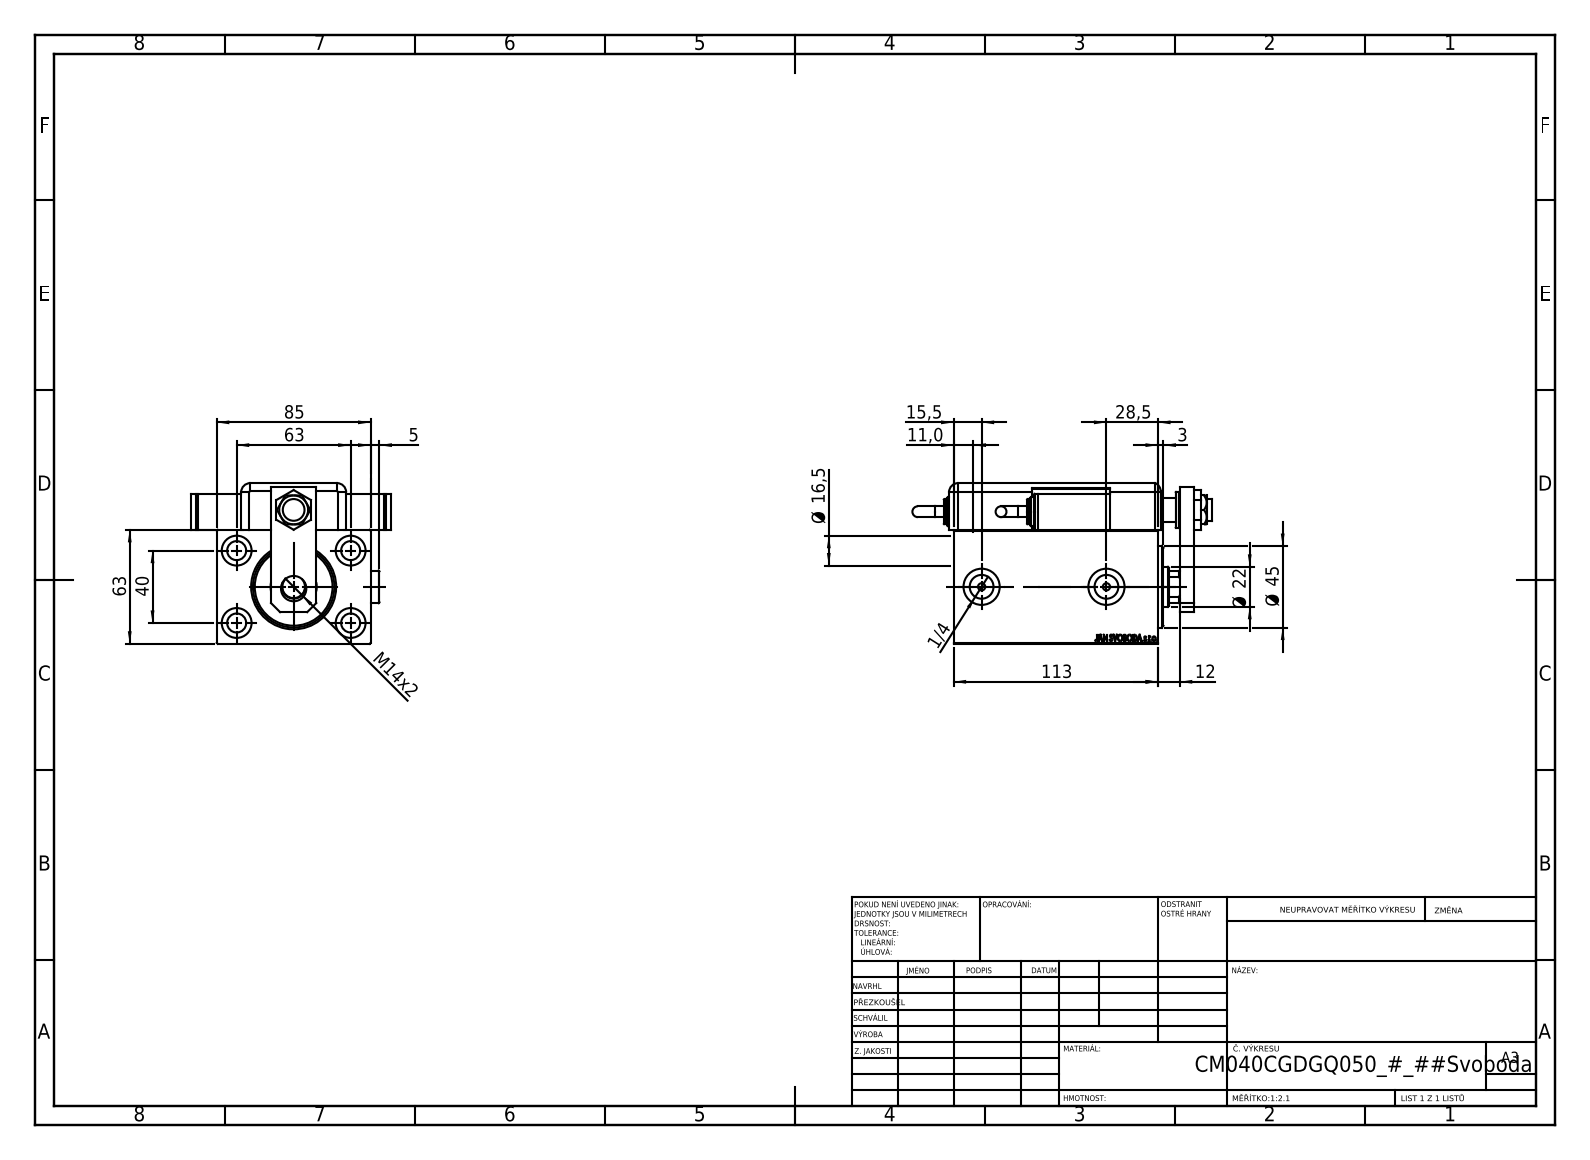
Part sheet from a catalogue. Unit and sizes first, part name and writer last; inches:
Units: inches
Overall size (bounding box): 6.514 × 4.37 × 3.496
Round holes (diameter × count): ⌀0.157 ×4, ⌀0.413 ×4, ⌀0.65 ×4, ⌀0.315 ×2, ⌀0.518 ×2, ⌀0.551 ×2, ⌀0.787 ×2, ⌀0.472 ×1, ⌀0.492 ×1, ⌀0.512 ×1, ⌀0.866 ×1, ⌀1.004 ×1
Round bosses / shafts (diameter × count): ⌀0.787 ×3, ⌀0.709 ×2, ⌀0.63 ×2, ⌀0.551 ×2, ⌀0.236 ×2
Partial cylindrical surfaces — rounded edges, fillets, slot ends (radius × count): R0.197 ×9, R0.394 ×1, R0.413 ×1
Main face-to-face distances: 0.118, 2.48, 0.531, 3.346, 0.472, 1.016, 3.496, 0.787, 4.449, 3.268
Hole centre spacings: 1.469, 1.448, 1.491, 1.524, 1.575, 2.48, 2.756, 2.938
Volume: 40.01 in³ · Surface area: 236.3 in²
Bodies: 15 solids, 1300 faces (648 planar, 131 cylindrical, 521 other)
Part name (STEP PRODUCT): KRYT; SWITCH DIM A_G; TYC; V450CM_C_Body (+7 more)
STEP written by: SolidWorks 2019 (CONFIG_CONTROL_DESIGN)
